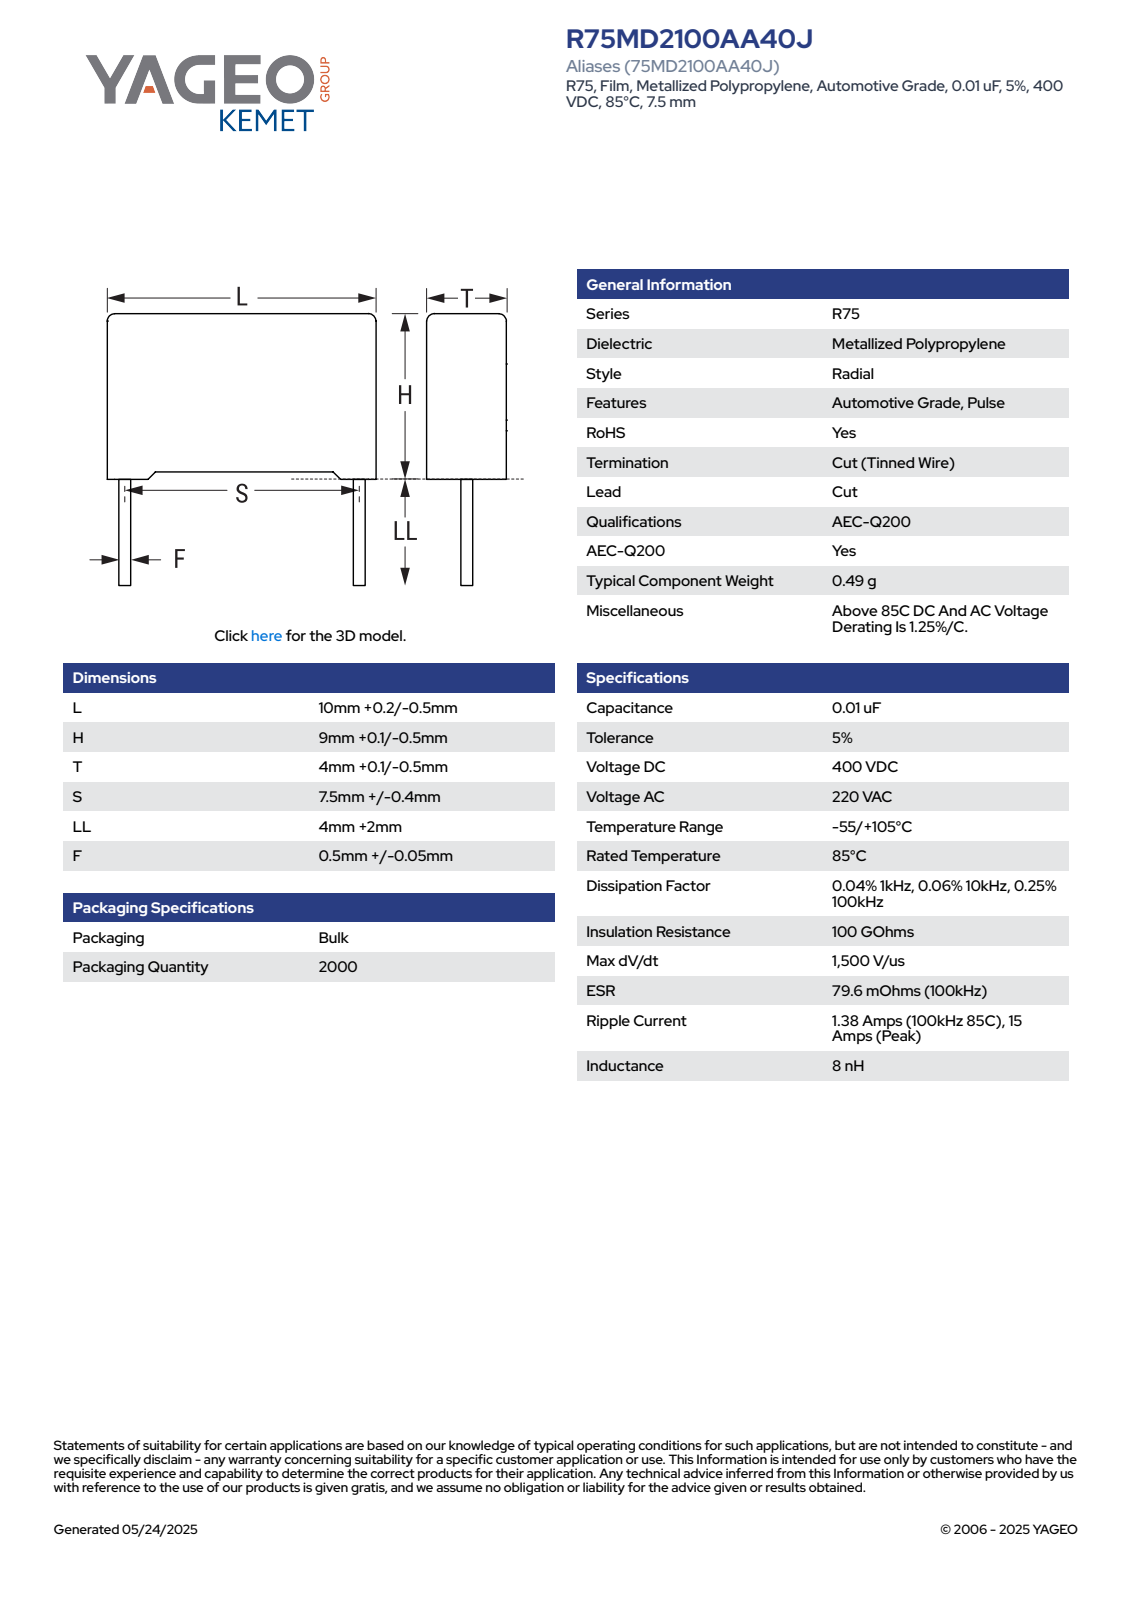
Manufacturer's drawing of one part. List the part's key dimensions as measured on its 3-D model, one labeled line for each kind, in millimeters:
Part name (STEP PRODUCT): CFR_RB2_10X9X4_L10.2H9.1T4.1S7.5LL6F0.55
STEP written by: SolidWorks 2021 (AUTOMOTIVE_DESIGN)
Units: millimetres
Bodies: 4 solids, 85 faces (77 planar, 8 cylindrical, 0 other)
Overall size (bounding box): 15.1 × 10.2 × 4.11
Volume: 357 mm³ · Surface area: 383 mm²
Round bosses / shafts (diameter × count): ⌀0.55 ×2
Partial cylindrical surfaces — rounded edges, fillets, slot ends (radius × count): R0.5 ×4
Main face-to-face distances: 4.1, 10.2, 8.35, 0.34, 3.76, 0.75, 9.1, 3.42, 9.86, 0.31
